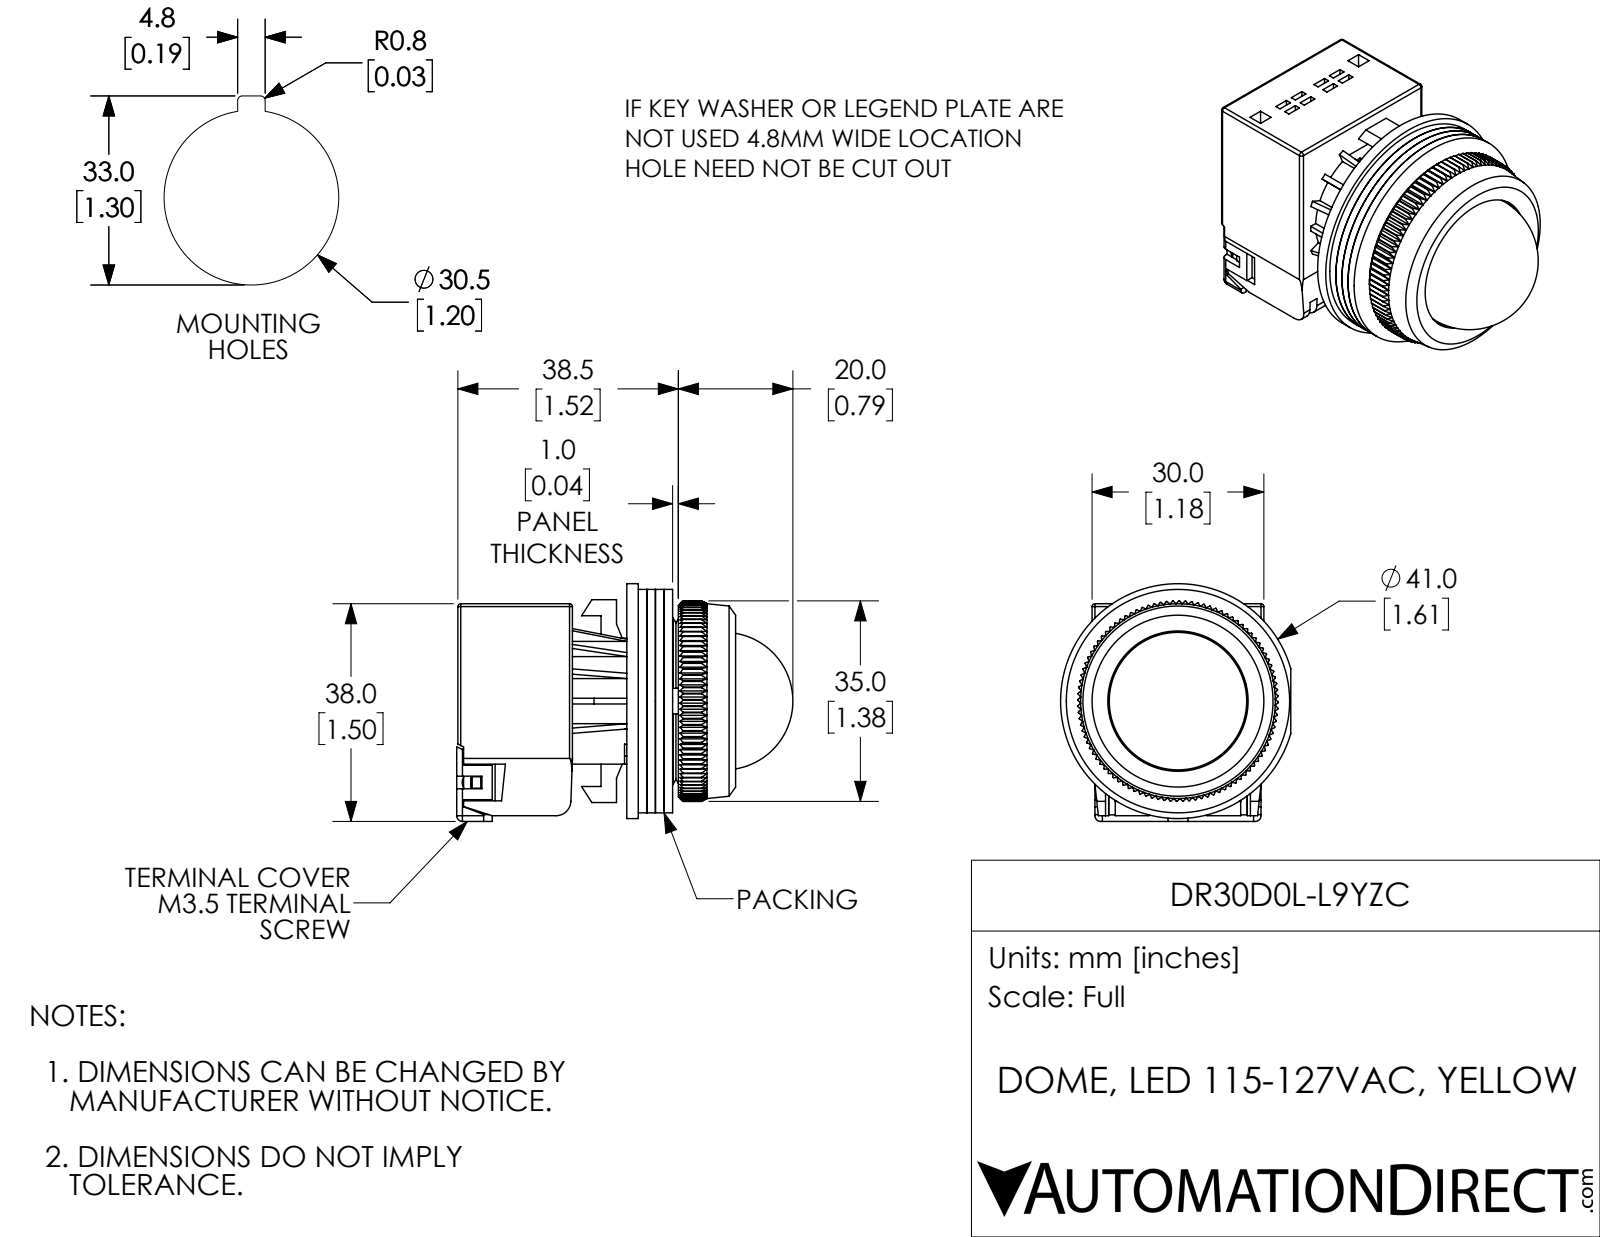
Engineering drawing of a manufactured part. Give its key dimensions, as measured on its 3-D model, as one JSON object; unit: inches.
{"part_name": "DR30D0L-L9YZC", "step_written_by": "SolidWorks 2017 (AUTOMOTIVE_DESIGN)", "units": "inches", "bodies": {"solids": 18, "faces": 1544, "planar": 945, "cylindrical": 353, "other": 246}, "overall_size": [2.309, 1.634, 1.583], "volume_in3": 2.184, "surface_area_in2": 48.71, "round_holes": [[0.118, 2], [0.122, 2], [0.138, 2], [0.276, 2], [0.362, 1], [0.433, 1], [0.461, 1], [0.543, 1], [0.563, 1], [0.583, 1], [0.63, 1], [0.72, 1]], "round_bosses_or_shafts": [[0.232, 2], [1.614, 1], [1.535, 1], [1.16, 1], [0.945, 1], [0.858, 1], [0.819, 1], [0.799, 1]], "partial_cylinders_radius": [[0.039, 14], [0.008, 8], [0.02, 8], [0.065, 3], [0.029, 1], [0.068, 1], [0.079, 1], [0.102, 1]], "face_to_face_distances": [0.059, 0.118, 0.177, 0.039, 0.315, 0.197, 0.512, 0.689, 0.374, 1.161], "hole_center_spacings": [0.704, 0.63]}
